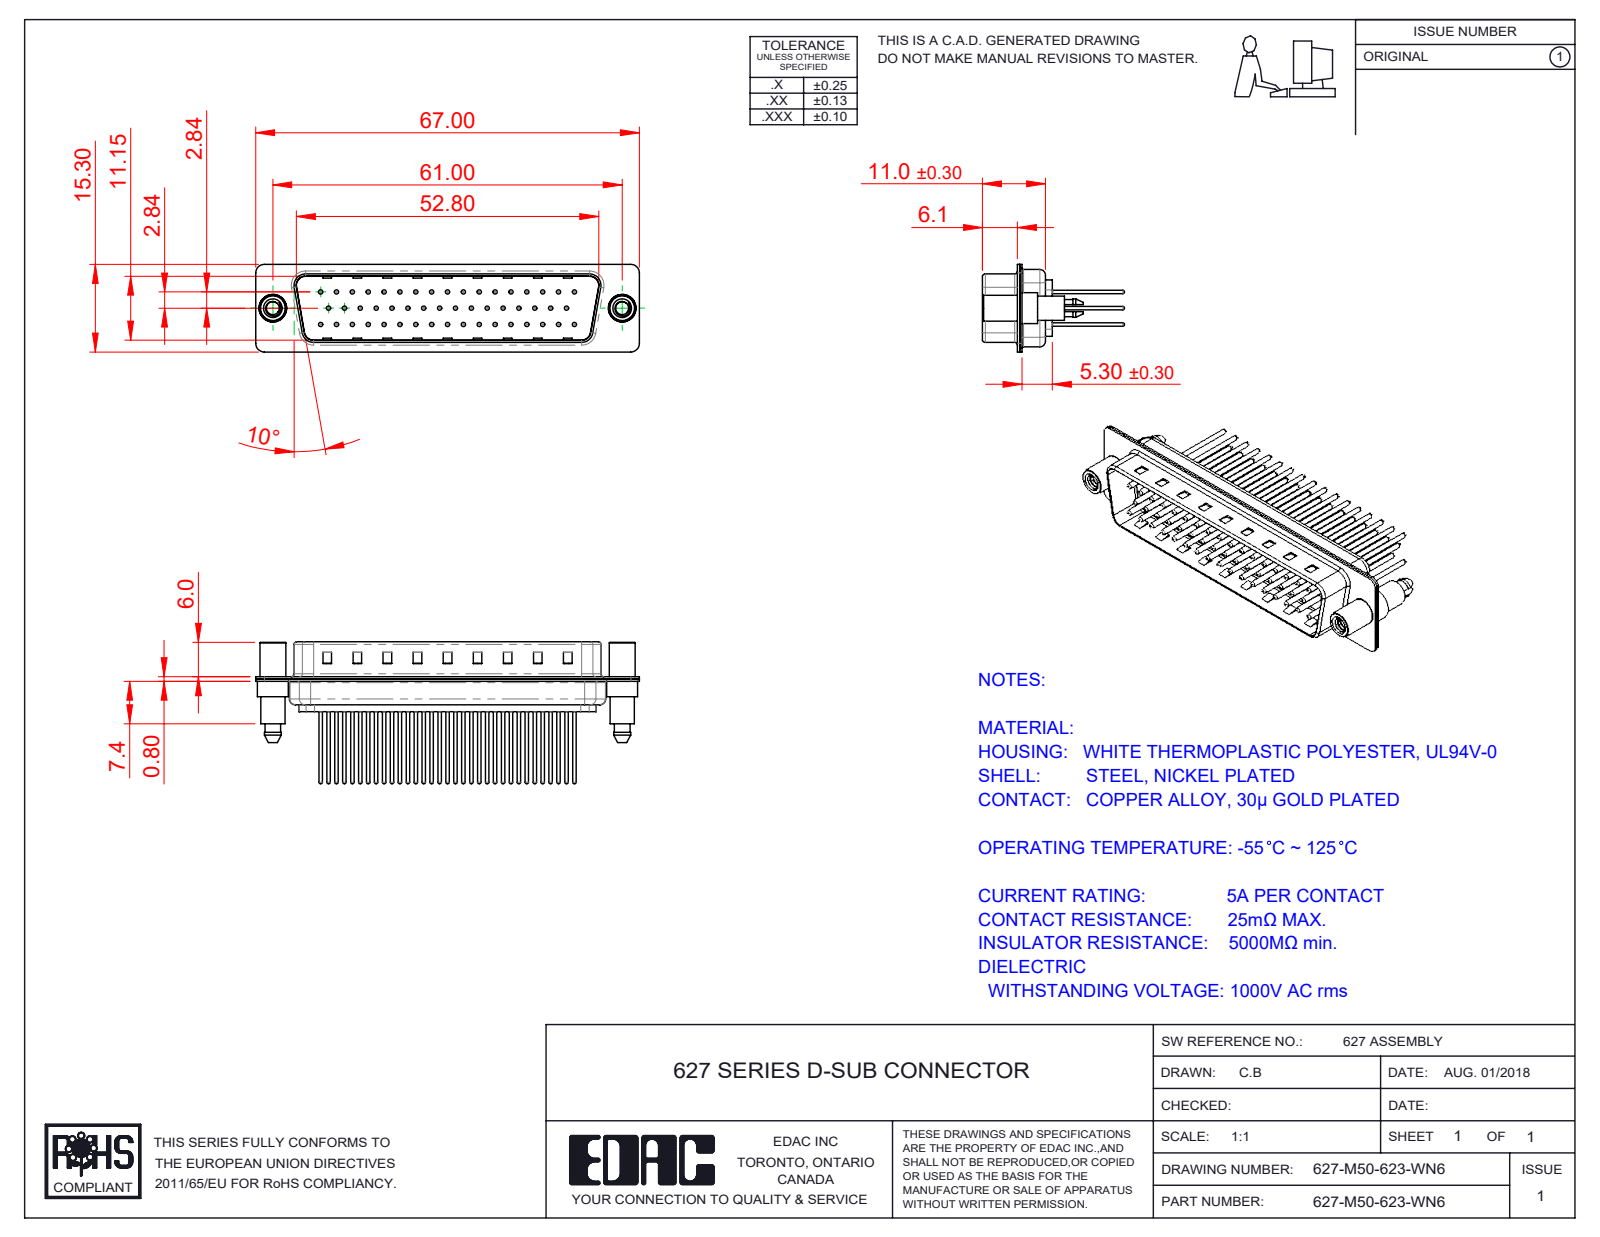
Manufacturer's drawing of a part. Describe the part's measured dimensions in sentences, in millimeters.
The part is named "627M Shell Rear_50 Contacts; 627M 4-40 Threaded Standoff and Boardlock; 627M Contact Row 2_23; 627-M50-623-WN6 (+4 more)". Its 3-D file was written by "SolidWorks 2020 (CONFIG_CONTROL_DESIGN)". It is 55 solids with 2314 faces: 571 planar, 869 cylindrical and 874 other. Overall it measures 67 by 24.77 by 15.3 millimeters. Its volume is 4 960 cubic millimeters and its surface area 11 815 square millimeters. Round holes: 50 of diameter 0.75, 50 of diameter 1.6, 50 of diameter 2, 2 of diameter 2.26, 2 of diameter 4, 2 of diameter 4.8. Round bosses or shafts: 50 of diameter 1.5, 50 of diameter 0.6, 2 of diameter 5.4, 2 of diameter 4.9, 2 of diameter 4.5, 2 of diameter 4.25. Partial cylindrical surfaces (rounded edges, fillets, slot ends): 18 of radius 1.5, 12 of radius 2, 10 of radius 1.6, 8 of radius 0.5, 4 of radius 0.25, 4 of radius 0.6, 4 of radius 0.65, 4 of radius 0.9. The main face-to-face distances are 0.4, 11.55, 5.7, 6.1, 0.78, 0.77, 12.33, 5.3, 12.32, 13.1. The hole center spacings are 3.16, 2.77, 5.54, 8.31, 11.08, 13.85, 16.62, 5.03.
